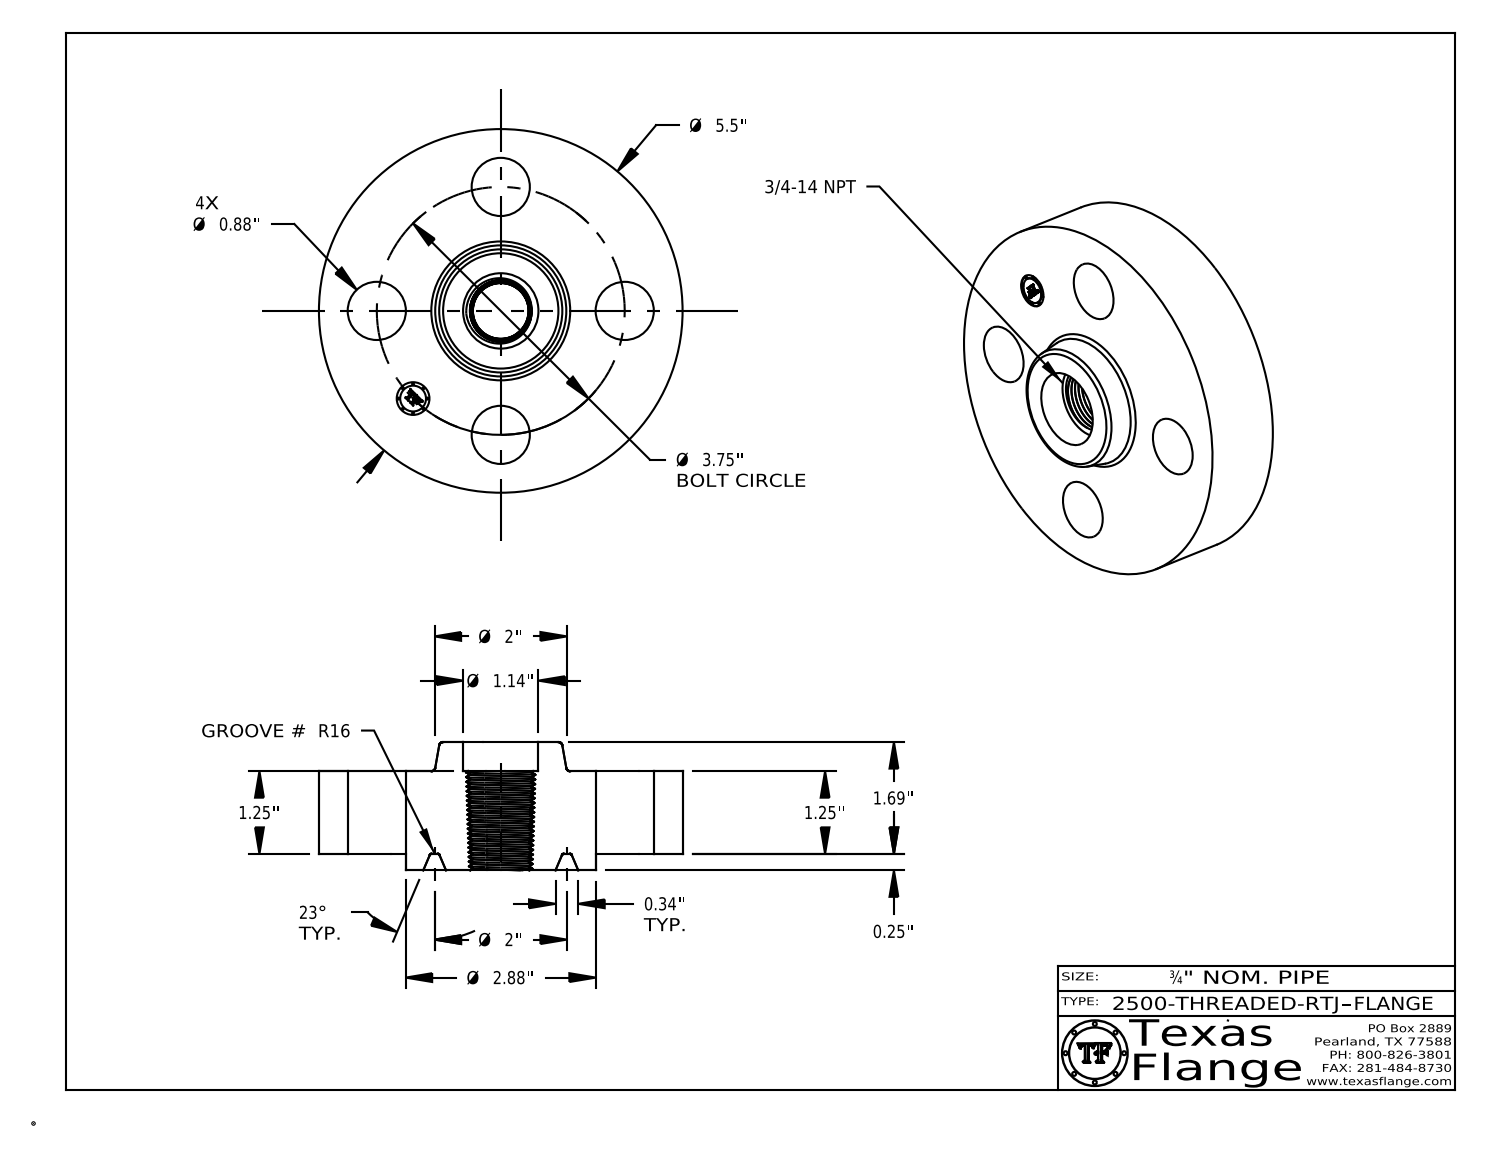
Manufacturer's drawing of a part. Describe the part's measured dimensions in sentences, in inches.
The part is named "2500-THREADED-RTJ". Its 3-D file was written by "CATIA V5 STEP AP214 (AUTOMOTIVE_DESIGN)". It is 1 solid with 642 faces: 372 planar, 38 cylindrical and 232 other. Overall it measures 5.5 by 5.5 by 1.94 inches. Its volume is 27.69 cubic inches and its surface area 92.96 square inches. Round holes: 4 of diameter 0.88, 1 of diameter 0.495, 1 of diameter 1.14. Round bosses or shafts: 8 of diameter 0.03, 1 of diameter 5.5, 1 of diameter 2.875, 1 of diameter 0.39. The main face-to-face distances are 1.25, 0.25, 1.5, 1.94, 1.69, 0.44, 1.485, 1.235, 0.015, 0.455. The hole center spacings are 1.875, 2.652, 1.435, 3.465, 3.75.
